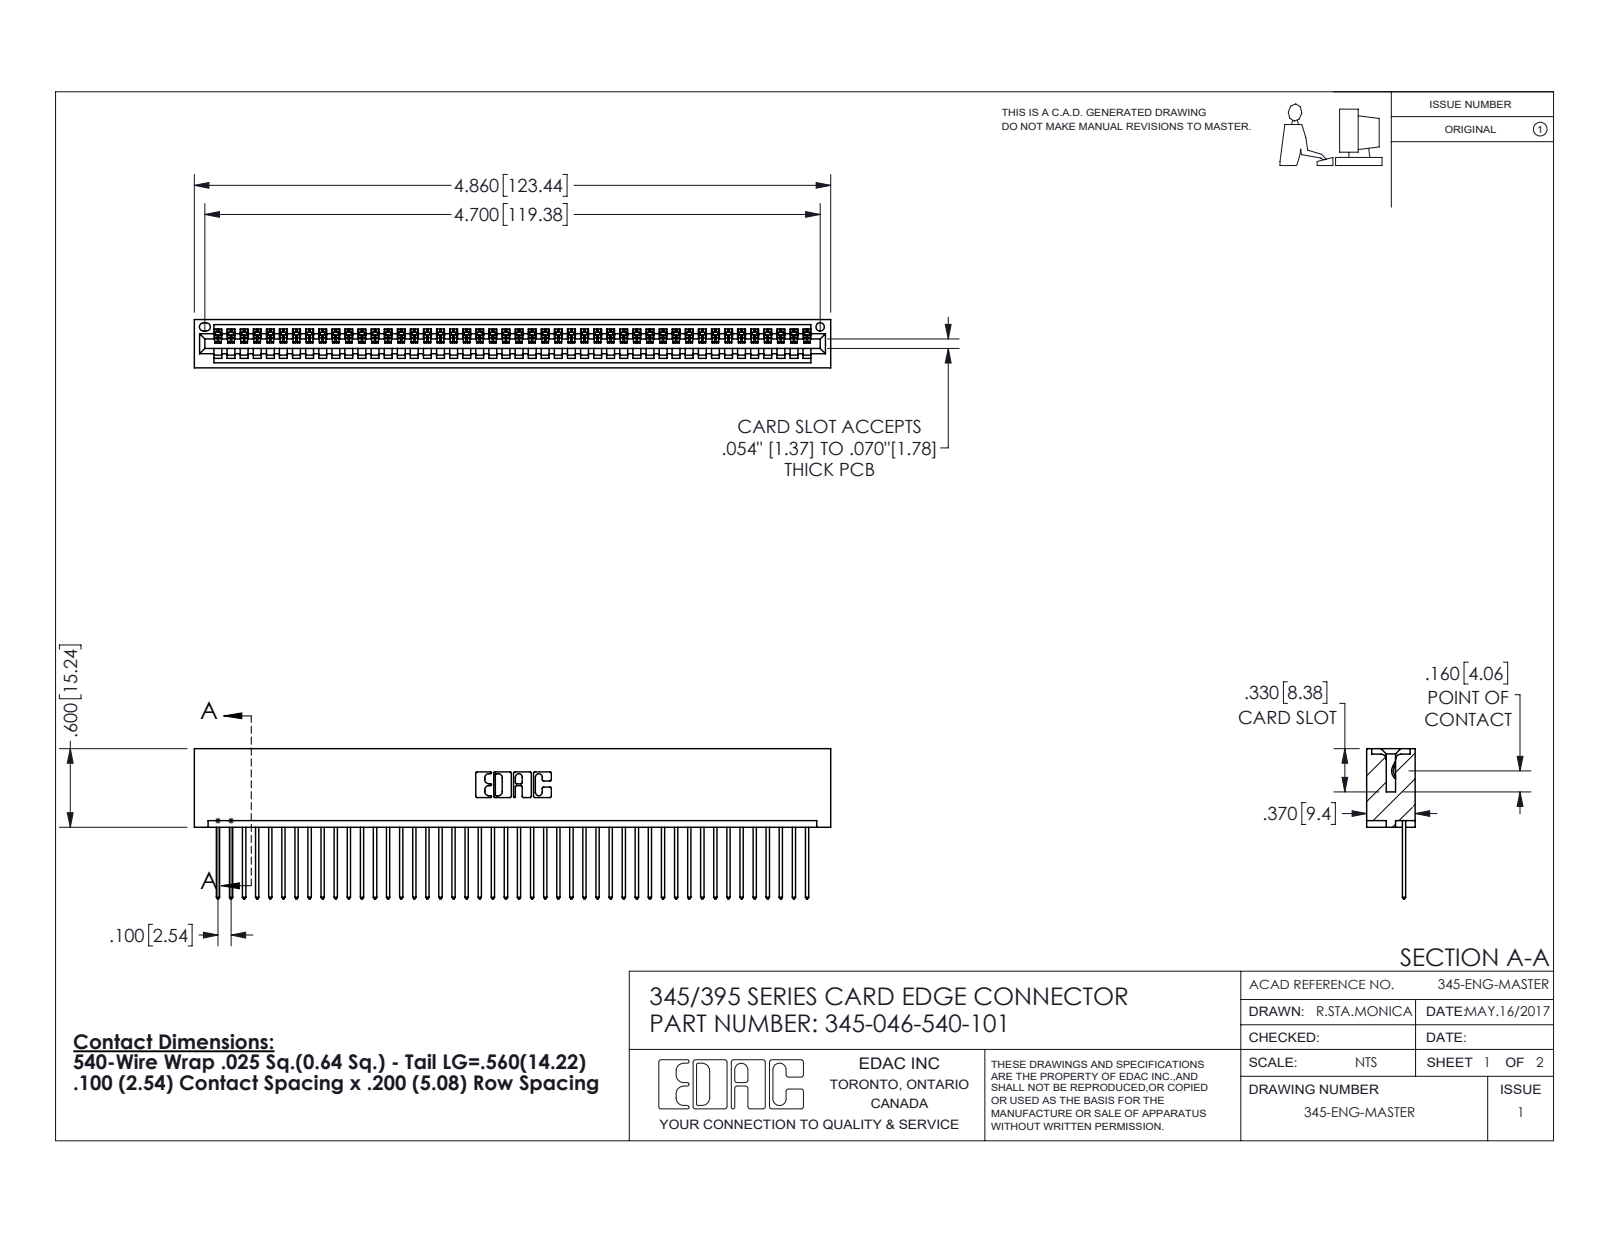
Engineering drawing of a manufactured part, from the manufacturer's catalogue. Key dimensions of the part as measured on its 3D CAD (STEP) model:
Part name (STEP PRODUCT): 345-046-540-101; 345-292-001_345-293-140; 345 Part_No Mounting Lugs
STEP written by: SolidWorks 2016 (CONFIG_CONTROL_DESIGN)
Units: inches
Bodies: 47 solids, 2786 faces (1916 planar, 870 cylindrical, 0 other)
Overall size (bounding box): 4.86 × 1.147 × 0.37
Volume: 0.757 in³ · Surface area: 26.62 in²
Round holes (diameter × count): ⌀0.064 ×1
Partial cylindrical surfaces — rounded edges, fillets, slot ends (radius × count): R0.006 ×92, R0.01 ×92, R0.01 ×22, R0.007 ×6, R0.031 ×6, R0.026 ×3, R0.031 ×2, R0.04 ×2
Main face-to-face distances: 0.072, 0.298, 0.098, 0.272, 0.025, 0.37, 0.2, 0.225, 0.149, 0.072
